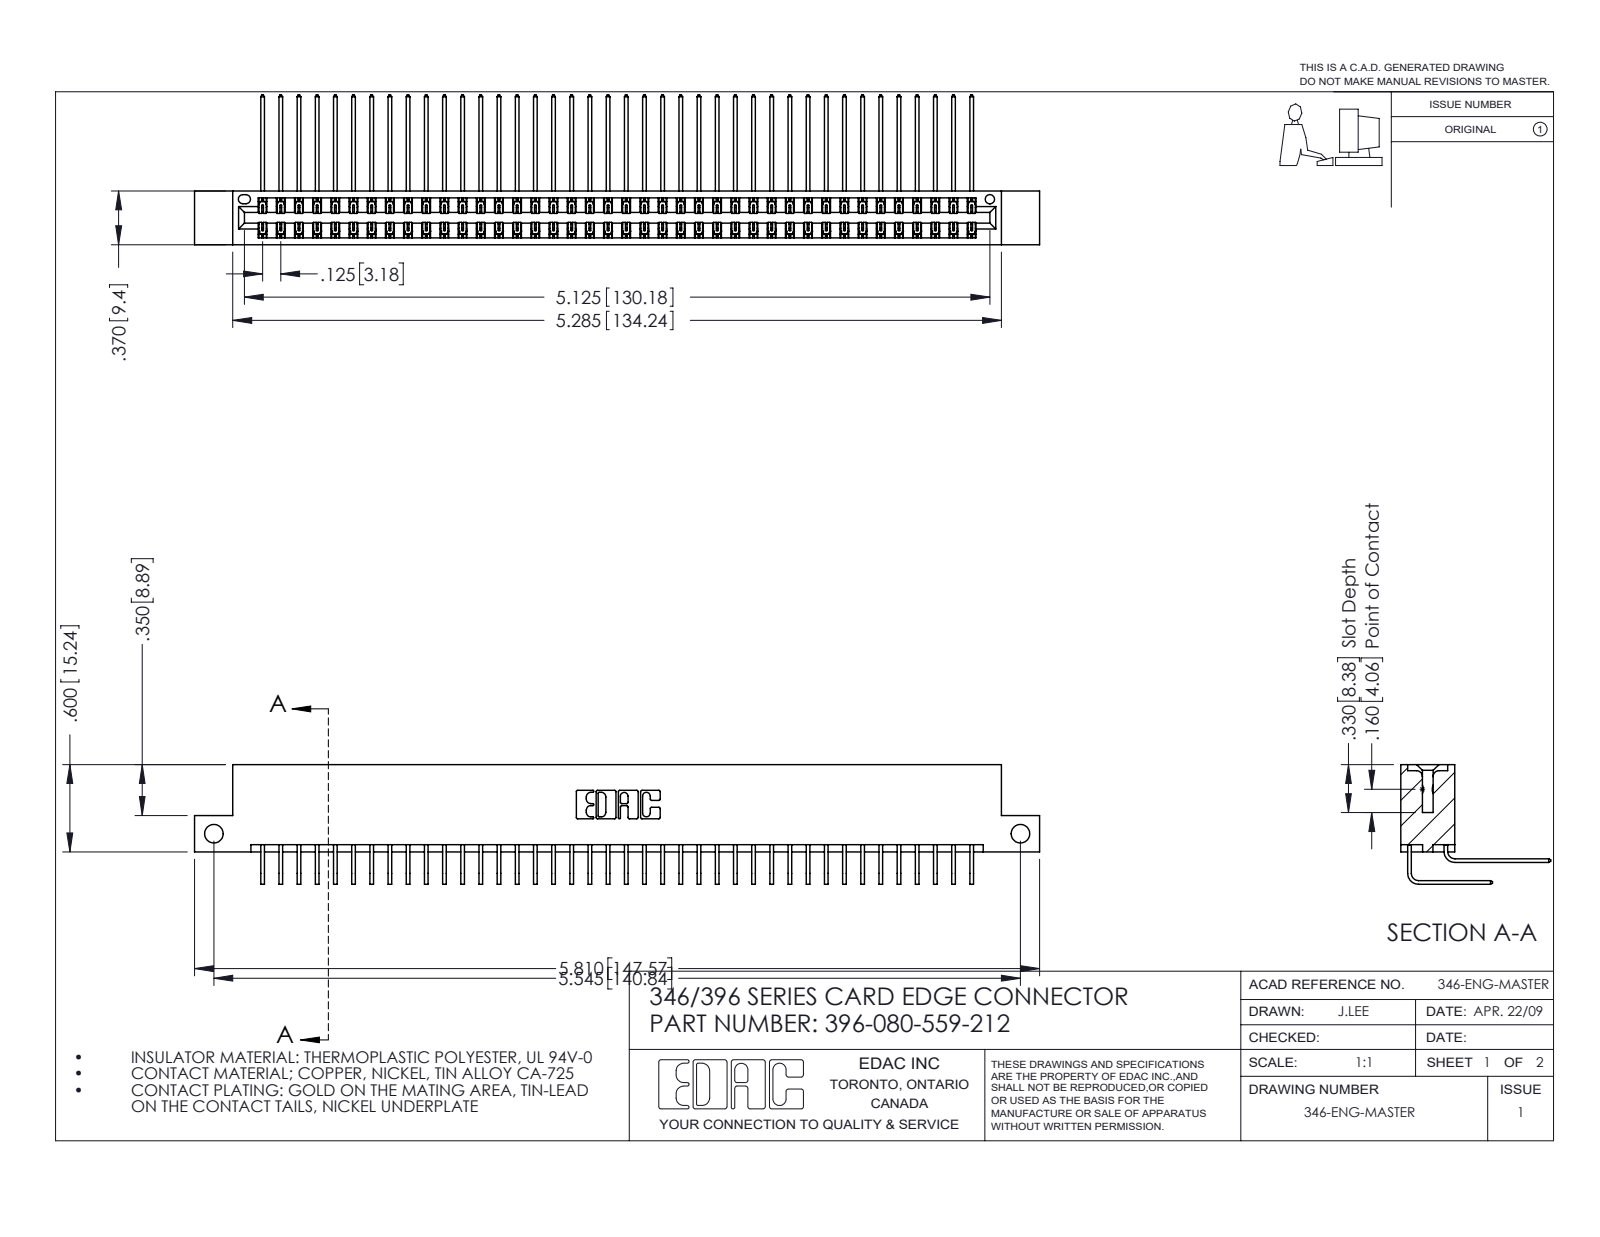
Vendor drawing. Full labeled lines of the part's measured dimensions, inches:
Part name (STEP PRODUCT): 345-292-001_558 559 Tail - 1; 396-080-559-212; 346 Part_Flush Mounting Lugs - Side Mount; 345-292-001_559 Tail - 2
STEP written by: SolidWorks 2016 (CONFIG_CONTROL_DESIGN)
Units: inches
Bodies: 81 solids, 4442 faces (3036 planar, 1406 cylindrical, 0 other)
Overall size (bounding box): 5.81 × 1.03 × 0.823
Volume: 0.9 in³ · Surface area: 34.59 in²
Round holes (diameter × count): ⌀0.128 ×2, ⌀0.064 ×1
Partial cylindrical surfaces — rounded edges, fillets, slot ends (radius × count): R0.006 ×120, R0.01 ×22, R0.007 ×6, R0.031 ×6, R0.026 ×3, R0.014 ×2, R0.022 ×2, R0.024 ×2
Main face-to-face distances: 0.048, 0.322, 0.025, 0.37, 0.25, 0.072, 0.298, 0.275, 0.148, 0.222
Hole centre spacings: 5.545
